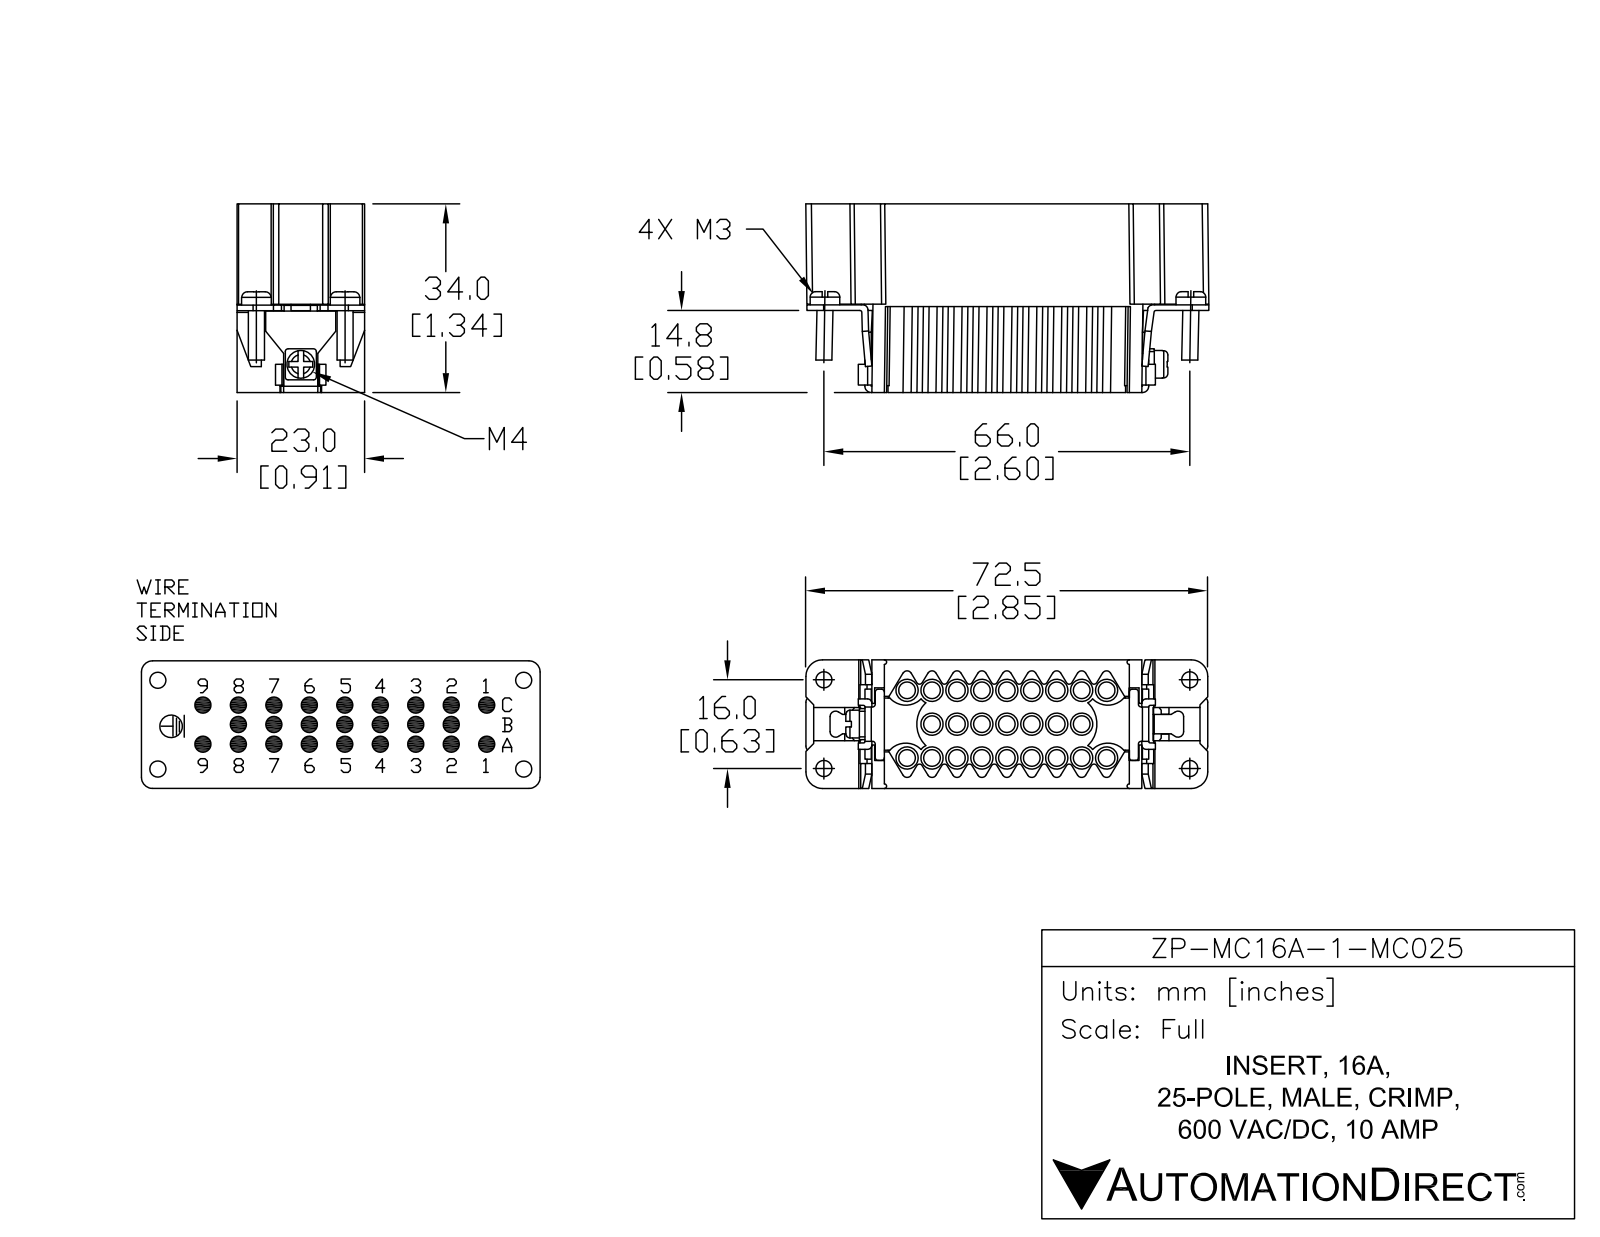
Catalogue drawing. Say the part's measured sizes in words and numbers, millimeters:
The part is named "ZP-MC16A-1-MC025". Its 3-D file was written by "SolidWorks 2014 (AUTOMOTIVE_DESIGN)". It is 20 solids with 705 faces: 403 planar, 291 cylindrical and 11 other. Overall it measures 72.5 by 32.2 by 23.2 millimeters. Its volume is 16 132 cubic millimeters and its surface area 22 617 square millimeters. Round holes: 25 of diameter 3, 25 of diameter 4, 1 of diameter 2.94. Round bosses or shafts: 4 of diameter 5.35, 4 of diameter 2.9, 1 of diameter 5. Partial cylindrical surfaces (rounded edges, fillets, slot ends): 18 of radius 0.85, 18 of radius 1, 16 of radius 0.5, 16 of radius 0.55, 6 of radius 0.75, 4 of radius 0.25, 4 of radius 0.41, 4 of radius 2.5. The main face-to-face distances are 2.4, 20.8, 2.25, 23.2, 46.45, 18.4, 3, 1.15, 16.3, 3.84. The hole center spacings are 7.58, 10.87, 4.5, 14.81, 9, 13, 13.5, 19.01.
